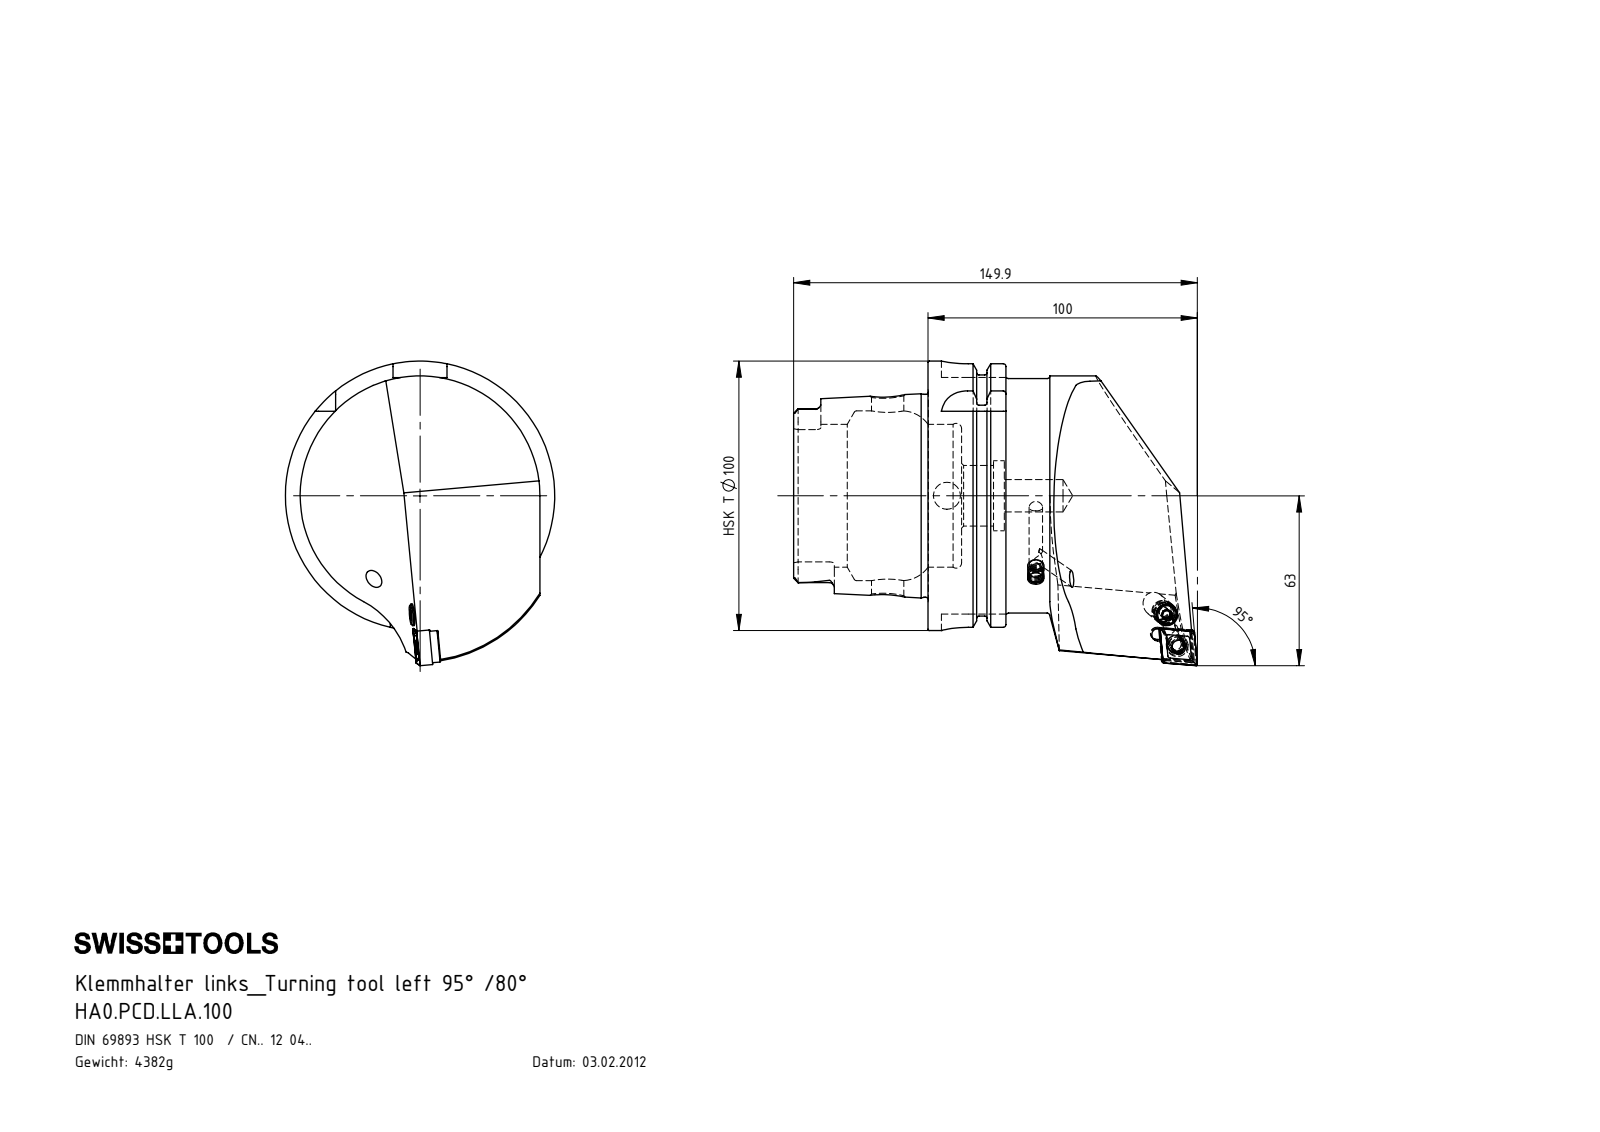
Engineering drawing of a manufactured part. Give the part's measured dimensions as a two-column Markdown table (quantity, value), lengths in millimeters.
| quantity | value |
| --- | --- |
| part name | HA0-PCD.LLA.100; WCD-ER3.101.000_A; WCD-ER4.101.017_A; WCD-ER2.101.003_A (+3 more) |
| STEP written by | SolidWorks 2012 (CONFIG_CONTROL_DESIGN) |
| units | millimeters |
| bodies | 7 solids, 368 faces (113 planar, 105 cylindrical, 150 other) |
| overall size | 149.9 × 113 × 100 |
| volume | 557 424 mm³ |
| surface area | 71 796 mm² |
| round holes (diameter × count) | 5 × 3, 12 × 2, 5.16 × 1, 6 × 1, 6.4 × 1, 7 × 1, 8.4 × 1, 10 × 1, 22.5 × 1, 26 × 1, 53 × 1, 63 × 1 |
| round bosses / shafts (diameter × count) | 100 × 1, 91.95 × 1, 87 × 1, 75.26 × 1, 8 × 1, 7.9 × 1, 6.4 × 1, 6 × 1 |
| partial cylindrical surfaces (radius × count) | 1.9 × 6, 0.4 × 4, 1 × 4, 10 × 4, 2.5 × 2, 4.83 × 2, 4.88 × 2, 2.1 × 1 |
| main face-to-face distances | 12.45, 28.95, 16.5, 49.9, 62.35, 78.85, 87.8, 78.2, 28.3, 15.85 |
| hole center spacings | 12.79, 12.84 |
